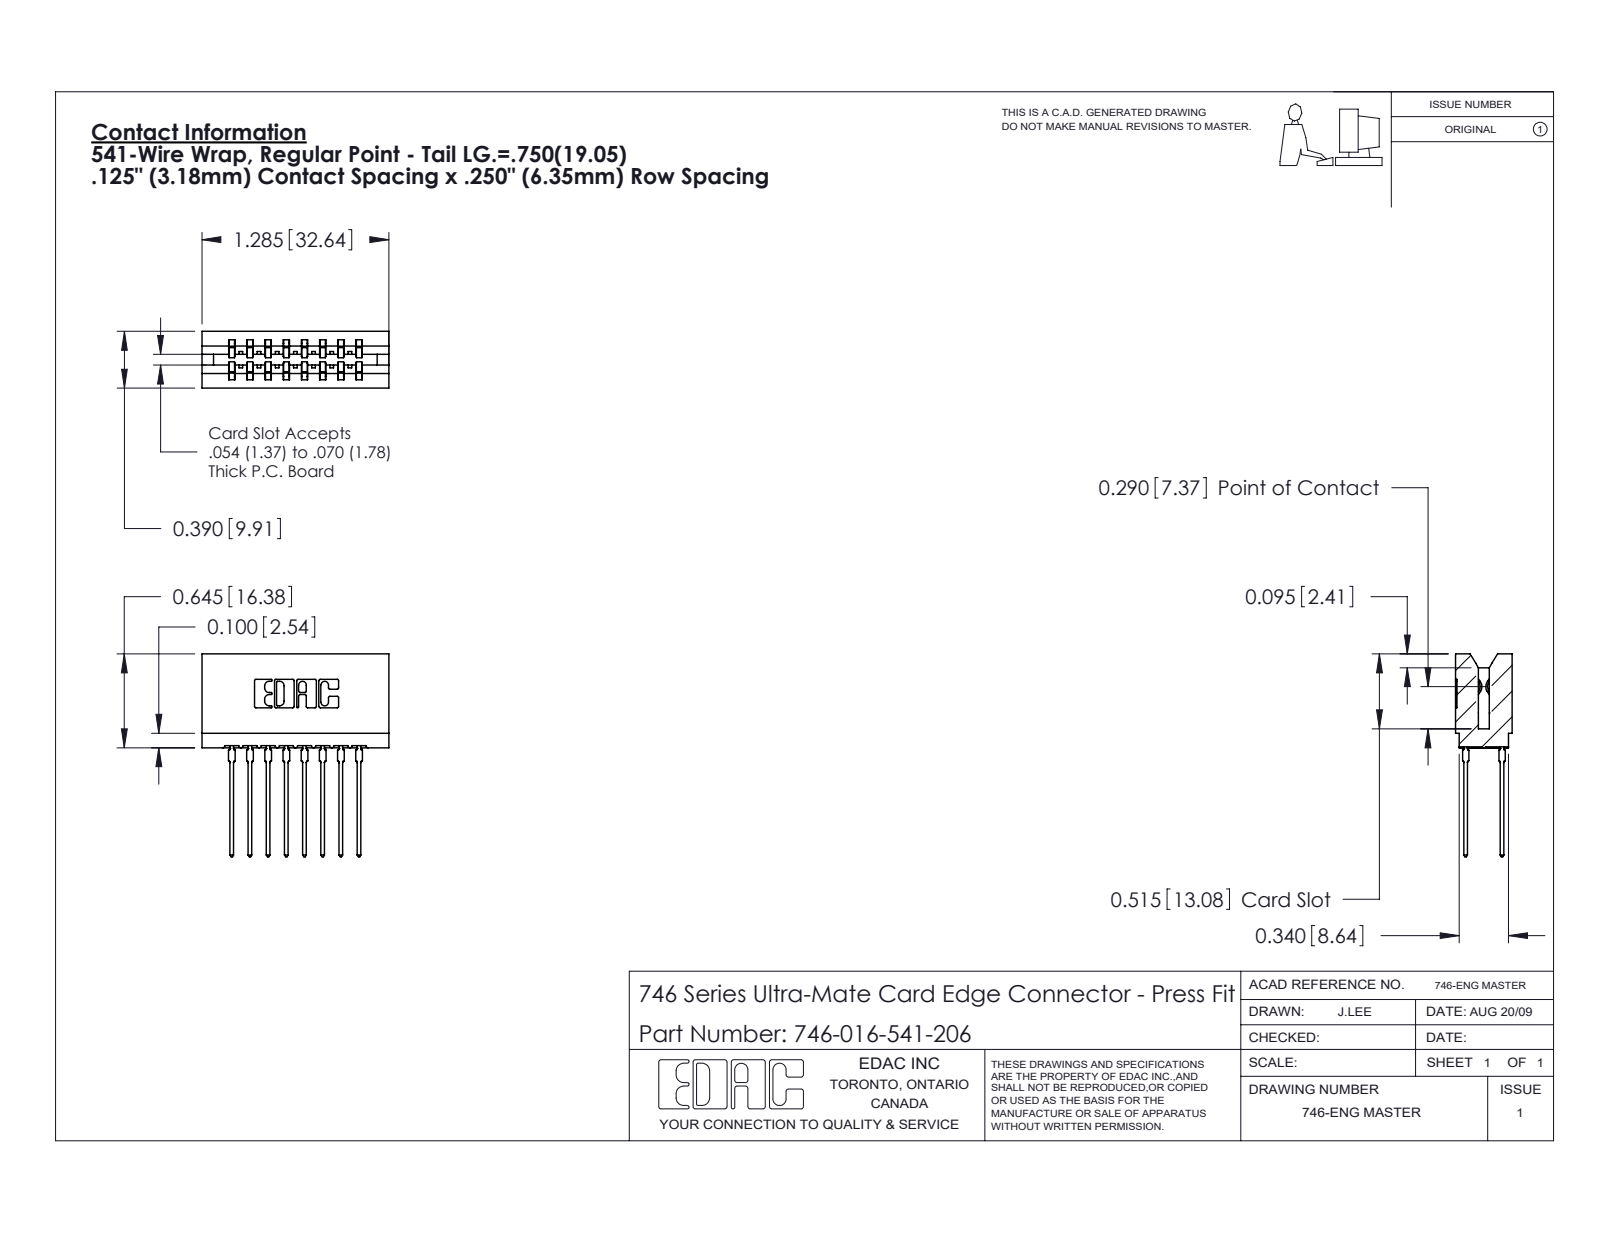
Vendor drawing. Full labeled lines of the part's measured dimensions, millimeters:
Part name (STEP PRODUCT): 746-016-541-206; 746 Part_.515 Slot Depth - 06; 746-292-001_541
STEP written by: SolidWorks 2020 (CONFIG_CONTROL_DESIGN)
Units: millimetres
Bodies: 17 solids, 1530 faces (792 planar, 322 cylindrical, 416 other)
Overall size (bounding box): 35.4 × 32.6 × 9.9
Volume: 3 790 mm³ · Surface area: 5 820 mm²
Partial cylindrical surfaces — rounded edges, fillets, slot ends (radius × count): R0.5 ×32, R0.3 ×22, R0.4 ×9, R0.1 ×8, R0.3 ×8, R0.2 ×6, R0.8 ×6, R0.7 ×3
Main face-to-face distances: 6.4, 8.5, 1.4, 3.2, 12.7, 1.1, 2.1, 7.4, 9.5, 5.3
